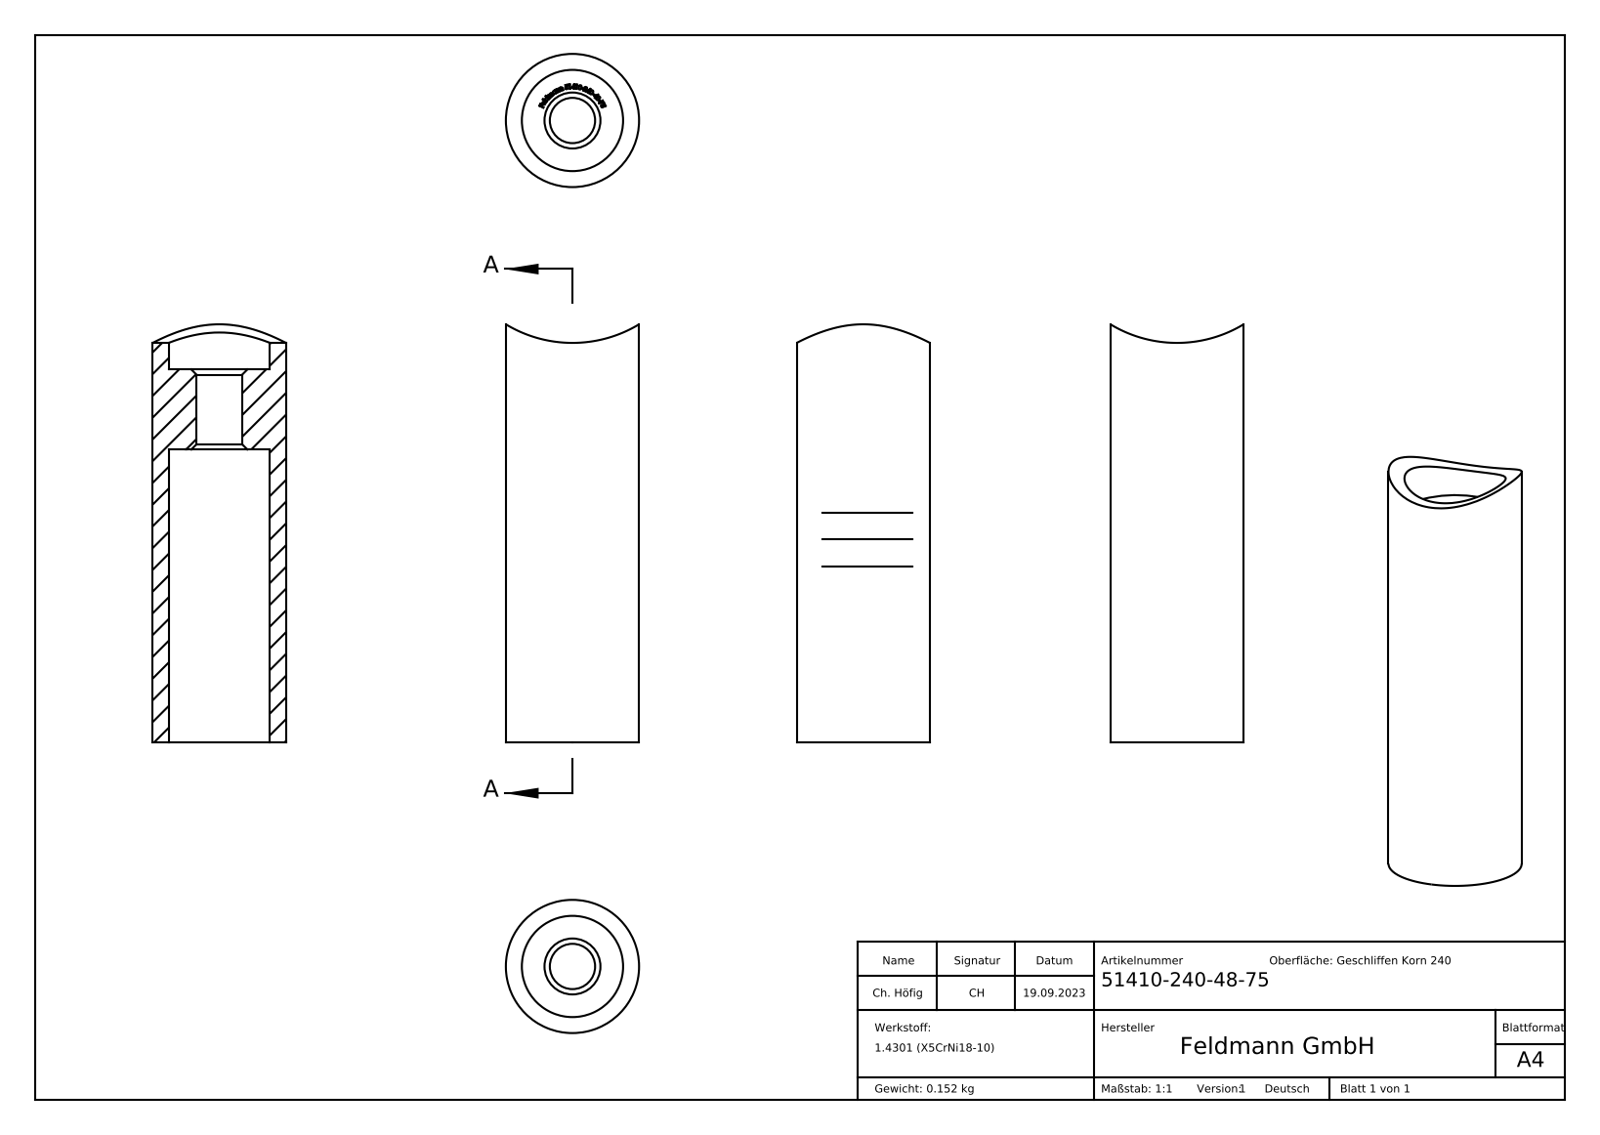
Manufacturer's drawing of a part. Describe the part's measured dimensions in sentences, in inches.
The part is named "51410-240-48-75". Its 3-D file was written by "SolidWorks 2018 (CONFIG_CONTROL_DESIGN)". It is 1 solid with 289 faces: 177 planar, 5 cylindrical and 107 other. Overall it measures 3.09 by 0.984 by 0.984 inches. Its volume is 1.172 cubic inches and its surface area 16.93 square inches. Round holes: 1 of diameter 0.335, 1 of diameter 0.748. Round bosses or shafts: 1 of diameter 0.984. Partial cylindrical surfaces (rounded edges, fillets, slot ends): 1 of radius 0.951. The main face-to-face distances are 2.756, 2.165, 0.591, 2.169, 0.587, 0.016, 0.017, 0.013, 0.019, 0.014.
